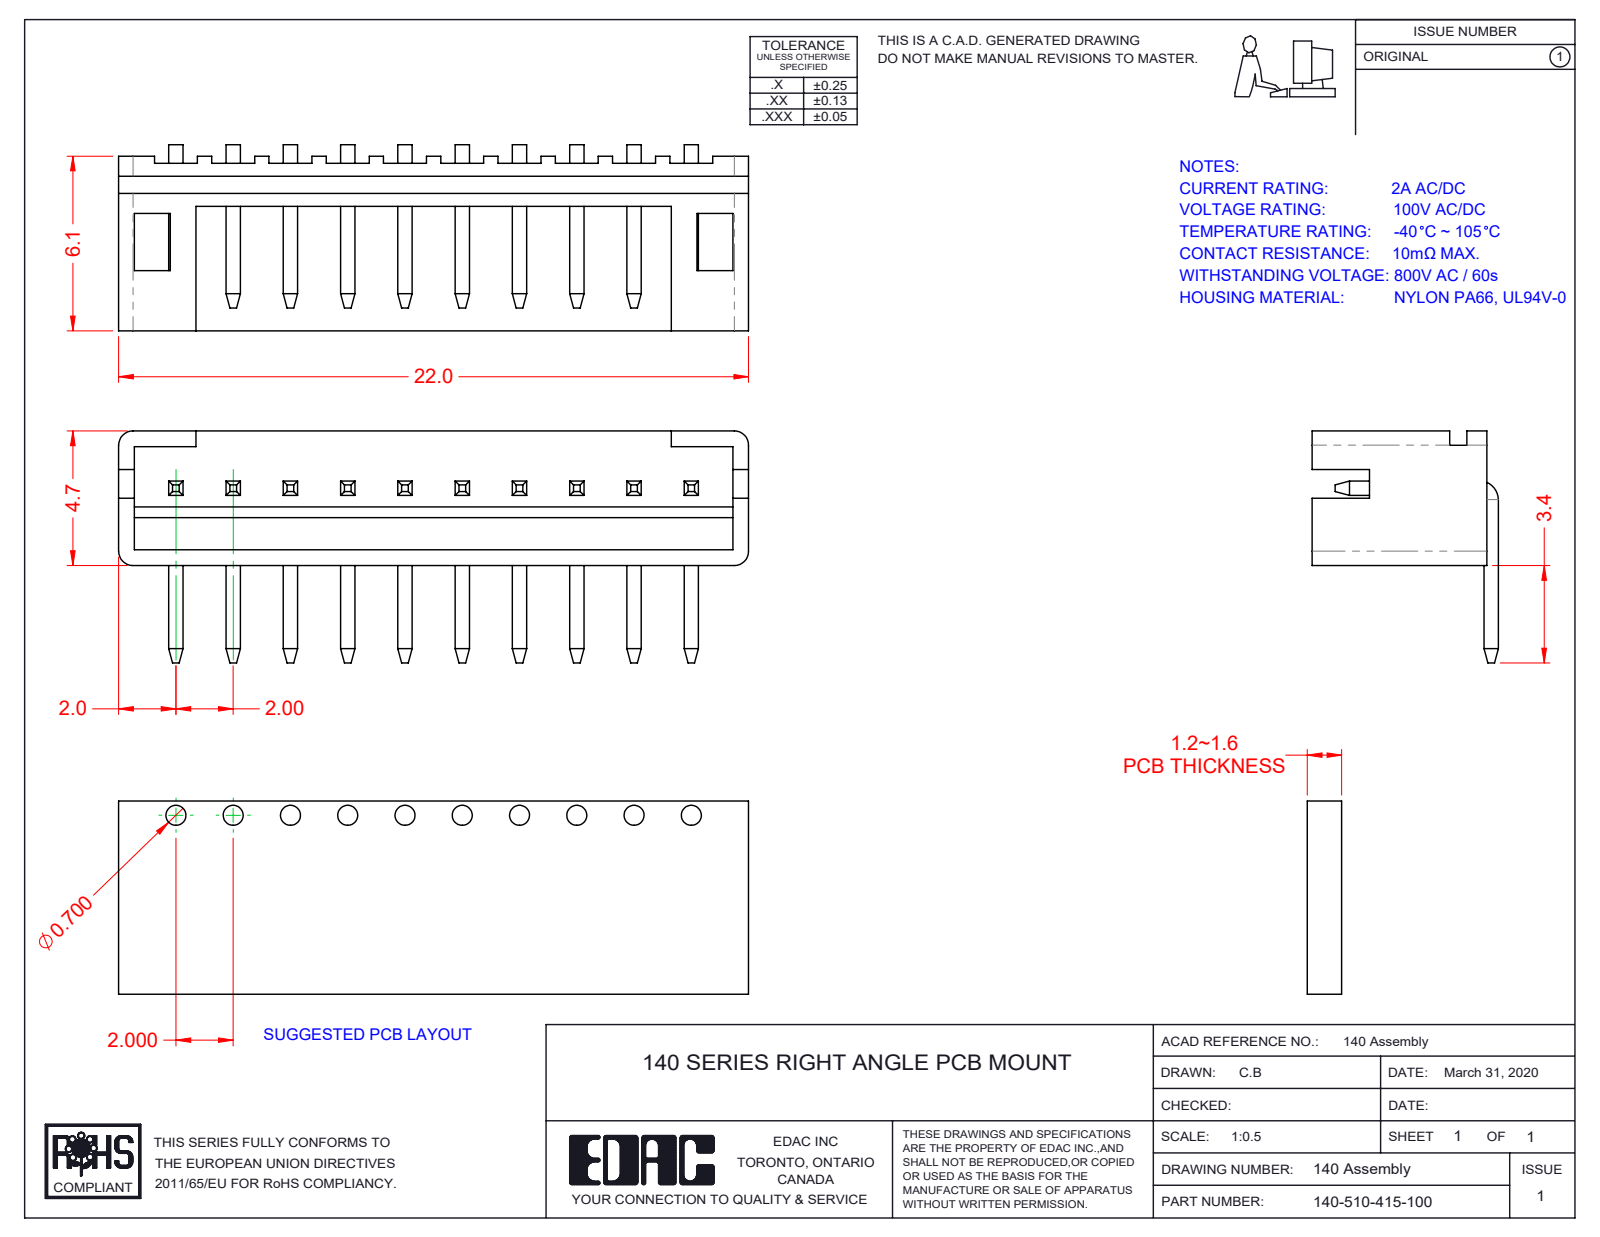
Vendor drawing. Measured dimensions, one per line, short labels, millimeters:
name: RA LI Contact_Str; 140-510-415-100; RA LI Housing_510
written by: SolidWorks 2020 (CONFIG_CONTROL_DESIGN)
unit: mm
bodies: 11 solids, 340 faces (314 planar, 26 cylindrical, 0 other)
size: 22 × 8.1 × 6.5
volume: 239 mm³; area: 903 mm²
rounds: 4× R0.5, 1× R0.15, 1× R0.65
face distances: 0.55, 0.5, 1.5, 2, 1.75, 6, 4, 0.65, 4.15, 8
